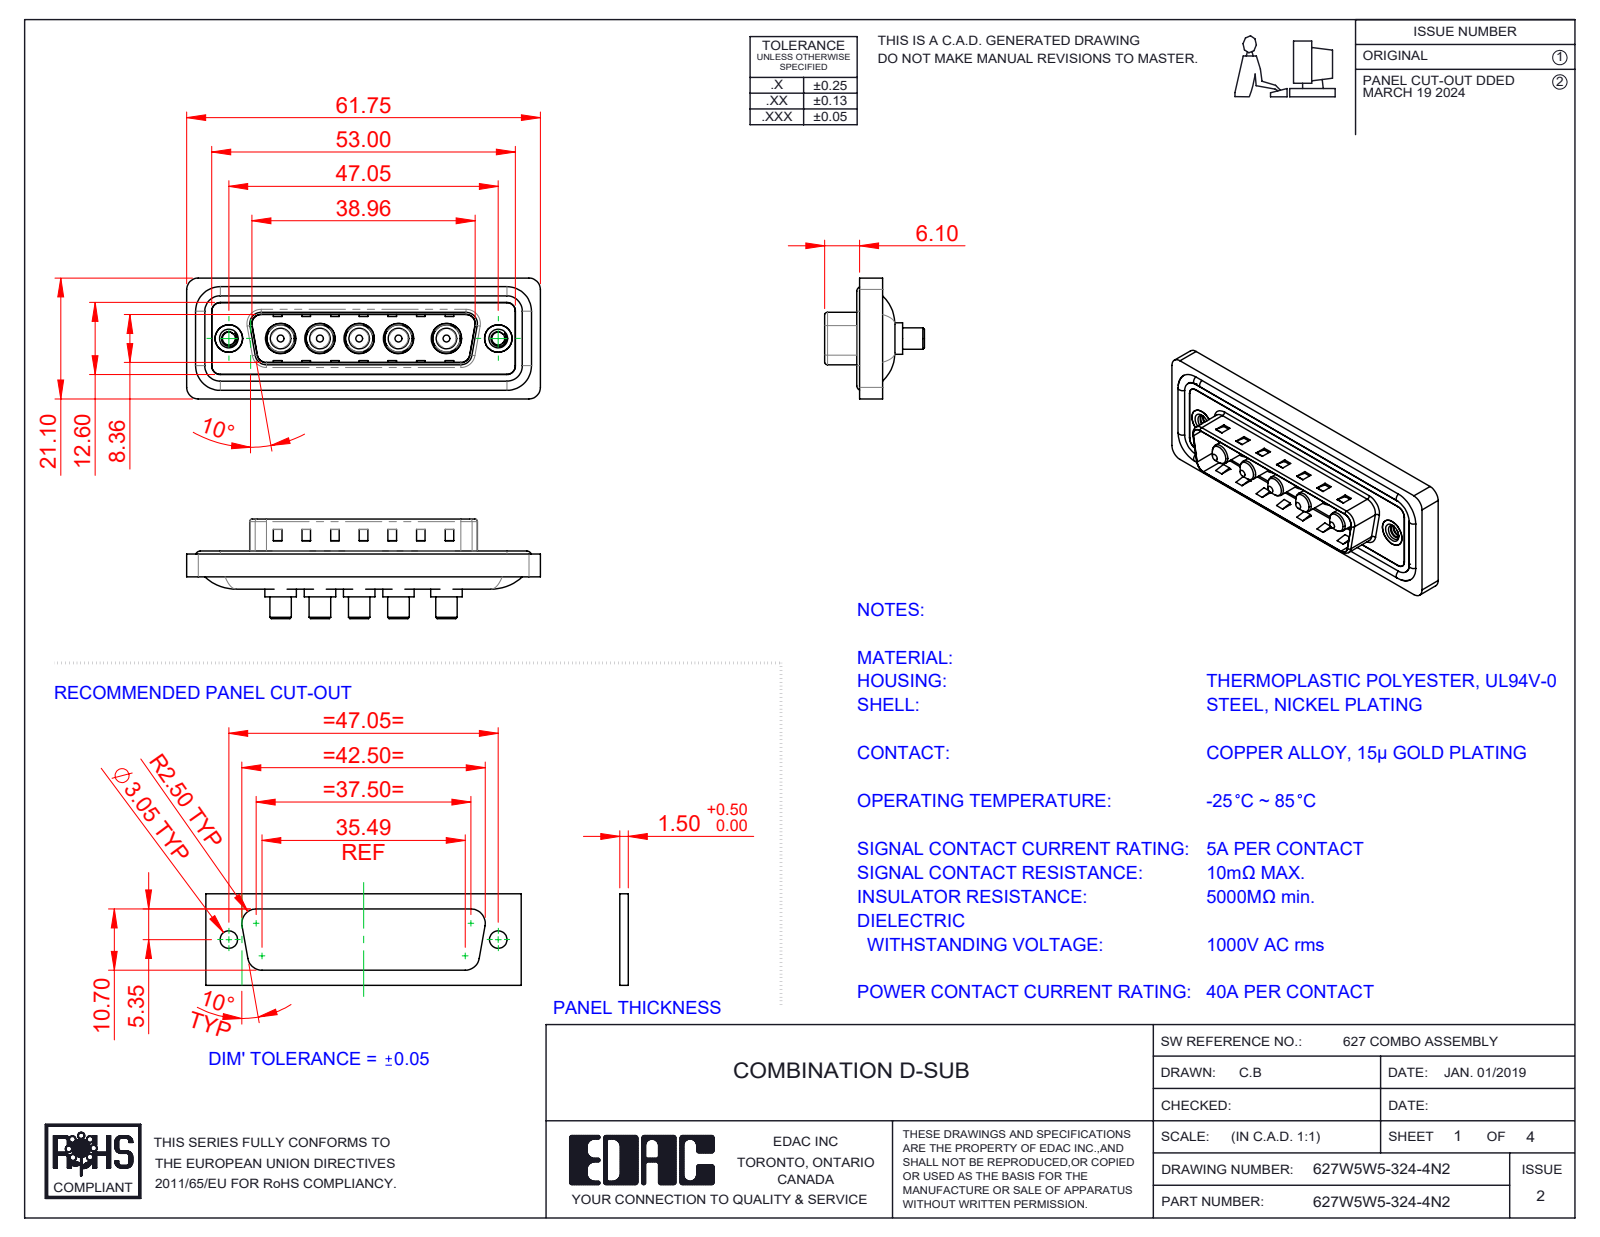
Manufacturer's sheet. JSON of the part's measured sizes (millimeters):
{"part_name": "627Combo Shell Front_25 Contacts; 627Combo Shell Rear_25 Contacts; 627W5W5-324-4N2; Power Pin_40A S (+3 more)", "step_written_by": "SolidWorks 2023 (CONFIG_CONTROL_DESIGN)", "units": "millimeters", "bodies": {"solids": 17, "faces": 678, "planar": 259, "cylindrical": 283, "other": 136}, "overall_size": [61.75, 21.1, 17.4], "volume_mm3": 7565, "surface_area_mm2": 11851, "round_holes": [[4.85, 5], [5.3, 5], [2.26, 2], [4, 2], [4.8, 2], [5, 2]], "round_bosses_or_shafts": [[5.5, 5], [5.2, 5], [4.75, 5], [3.75, 5], [3.6, 5], [1.6, 4], [4.9, 2]], "partial_cylinders_radius": [[1.5, 22], [2, 18], [0.5, 8], [1.6, 8], [2.1, 5], [0.25, 4], [0.6, 4], [0.65, 4]], "face_to_face_distances": [0.4, 1.5, 0.5, 1.1, 3.1, 1.6, 2.9, 0.82, 9.58, 5.65], "hole_center_spacings": [6.86, 9.04, 13.73, 38.01, 6.87, 8.37, 8.38, 9.05]}
